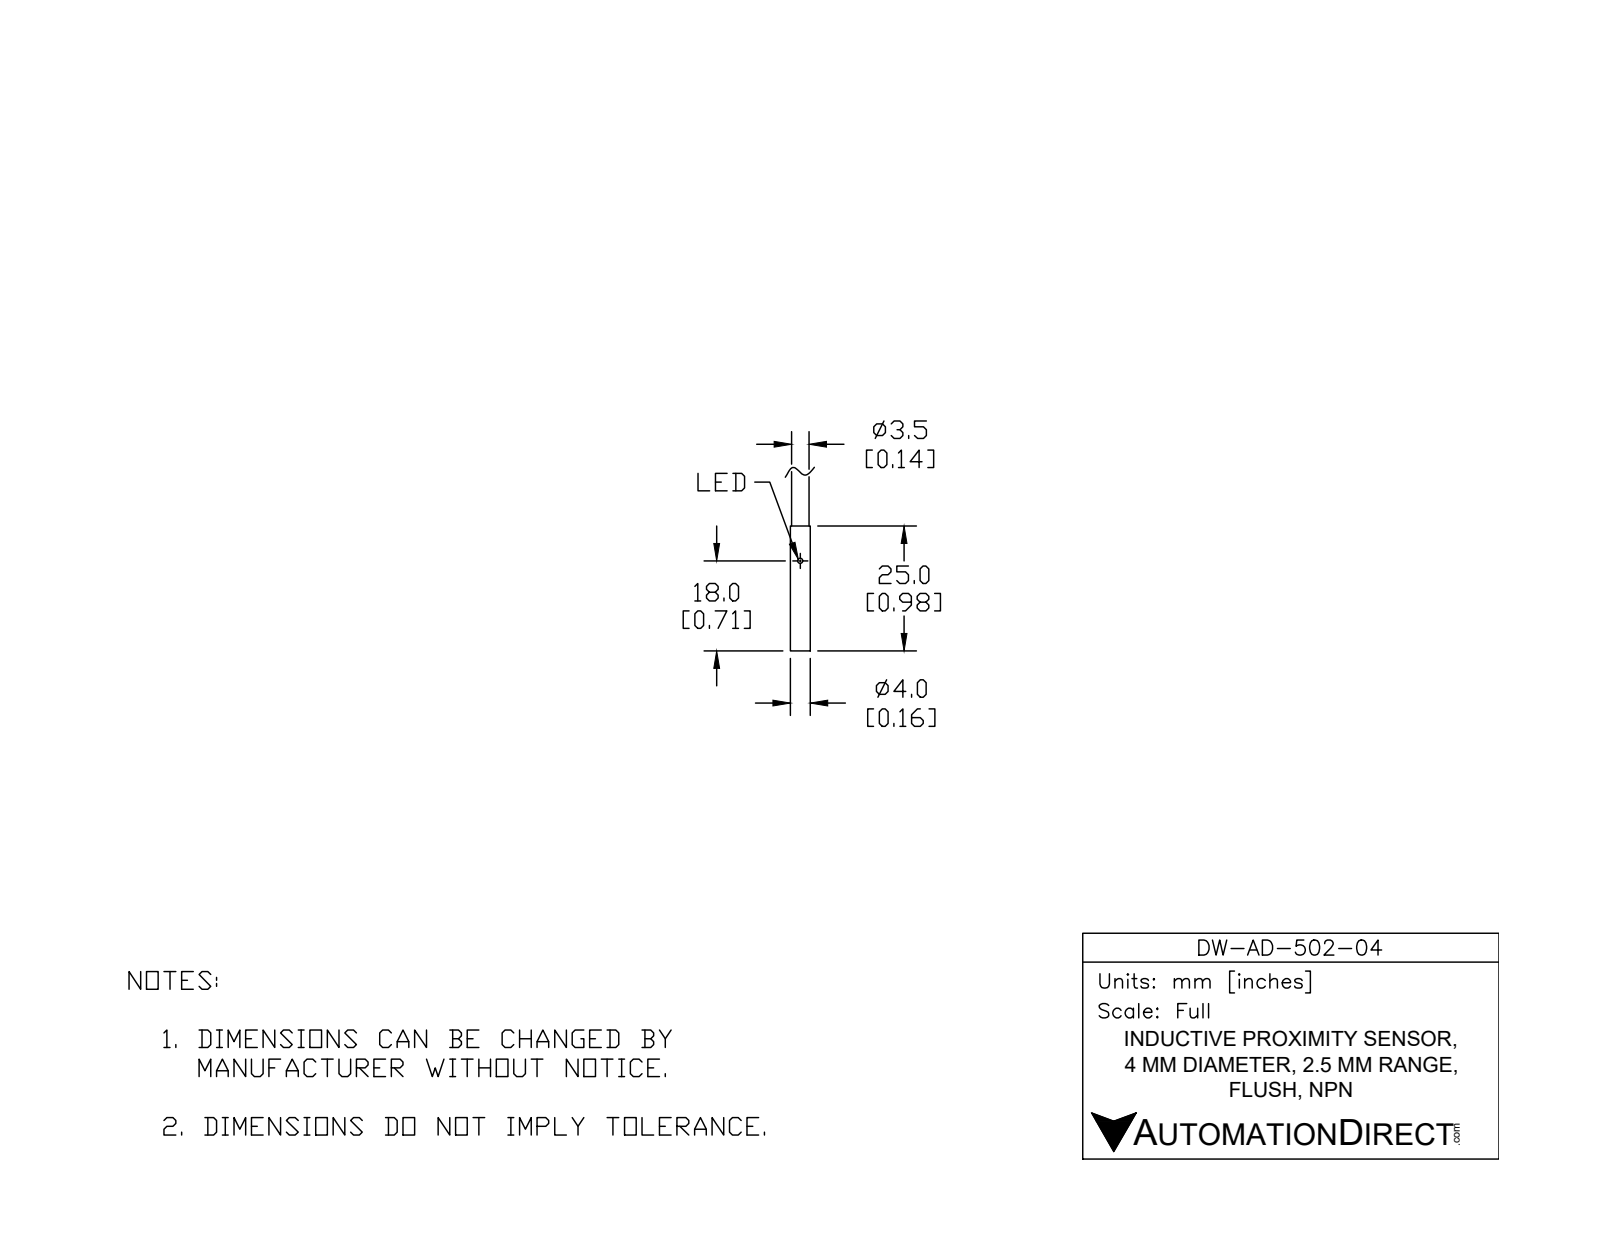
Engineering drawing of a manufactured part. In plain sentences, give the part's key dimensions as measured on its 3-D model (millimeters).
The part is named "DW-AD-501-04". Its 3-D file was written by "SolidWorks 2017 (AUTOMOTIVE_DESIGN)". It is 3 solids with 13 faces: 5 planar, 5 cylindrical and 3 other. Overall it measures 47.9 by 4 by 4 millimeters. Its volume is 340 cubic millimeters and its surface area 946 square millimeters. Round holes: 1 of diameter 1.5, 1 of diameter 3.6. Round bosses or shafts: 1 of diameter 4, 1 of diameter 3.5. The main face-to-face distances are 0.8, 20, 19.2, 25, 24.2, 5.
